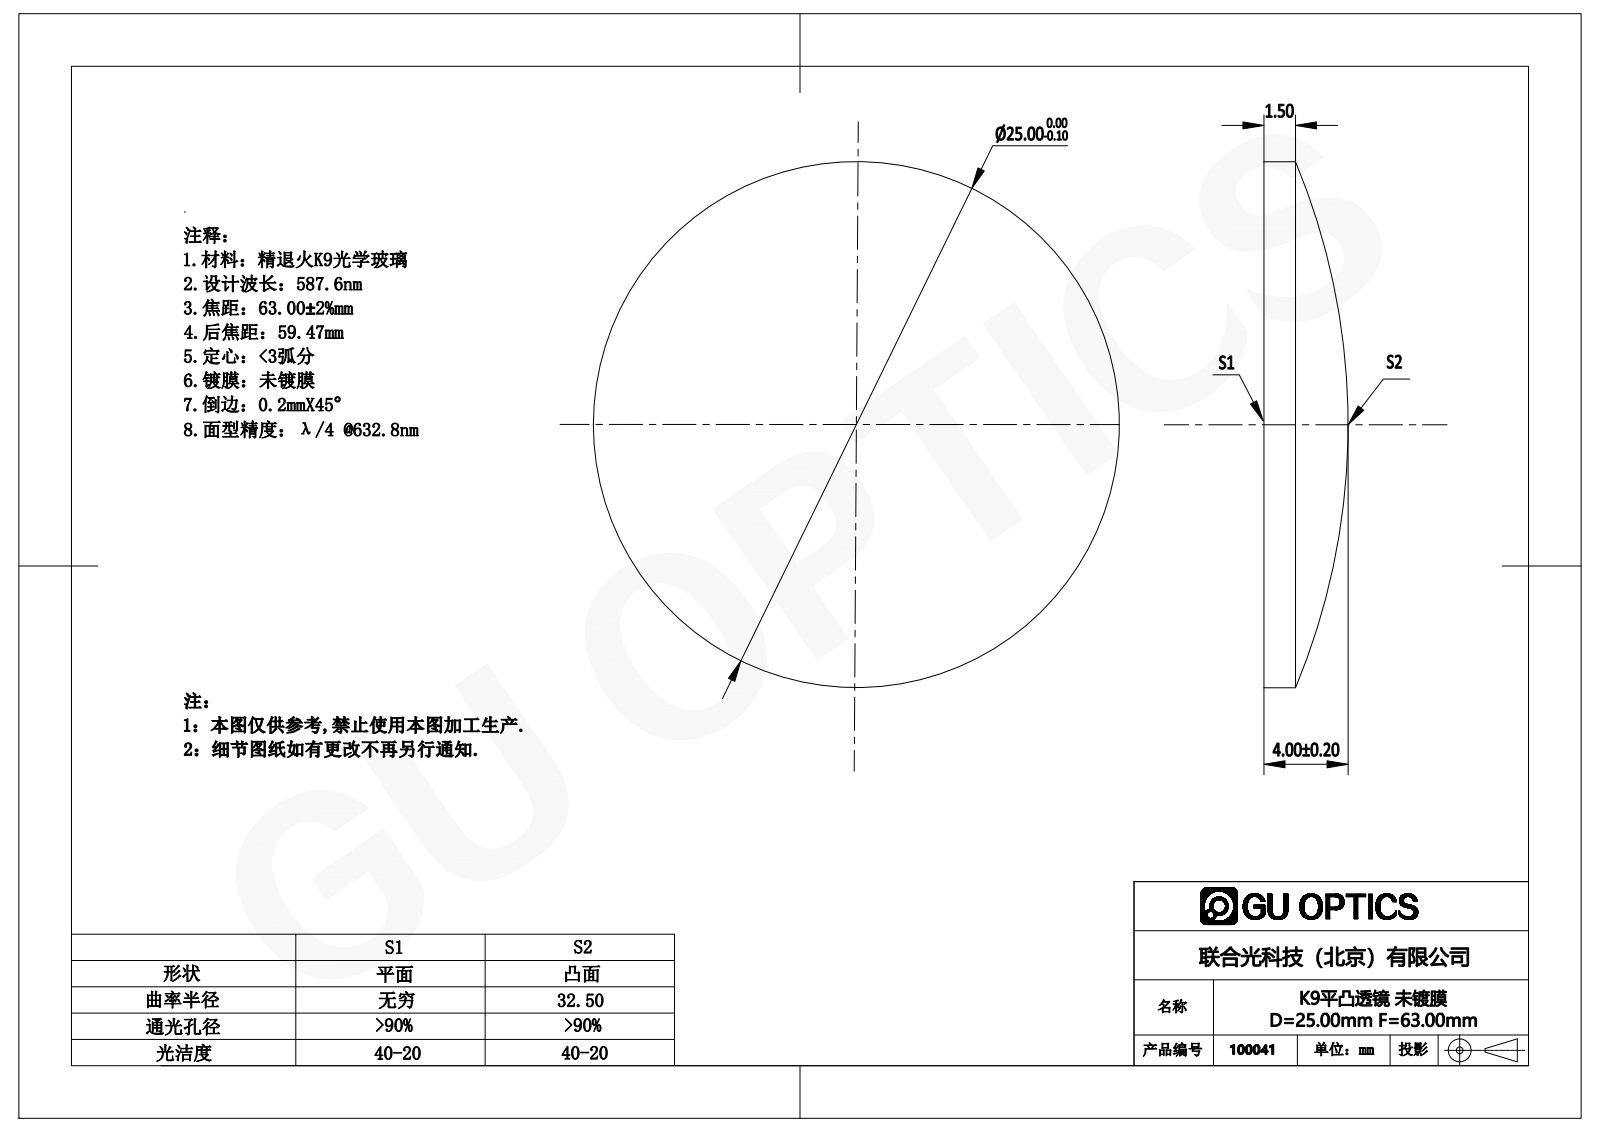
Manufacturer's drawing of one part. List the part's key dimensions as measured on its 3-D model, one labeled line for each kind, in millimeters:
Part name (STEP PRODUCT): 100041
STEP written by: SolidWorks 2016 (AUTOMOTIVE_DESIGN)
Units: millimetres
Bodies: 1 solid, 5 faces (1 planar, 2 cylindrical, 2 other)
Overall size (bounding box): 25 × 25 × 4
Volume: 1 358 mm³ · Surface area: 1 119 mm²
Round bosses / shafts (diameter × count): ⌀25 ×1
